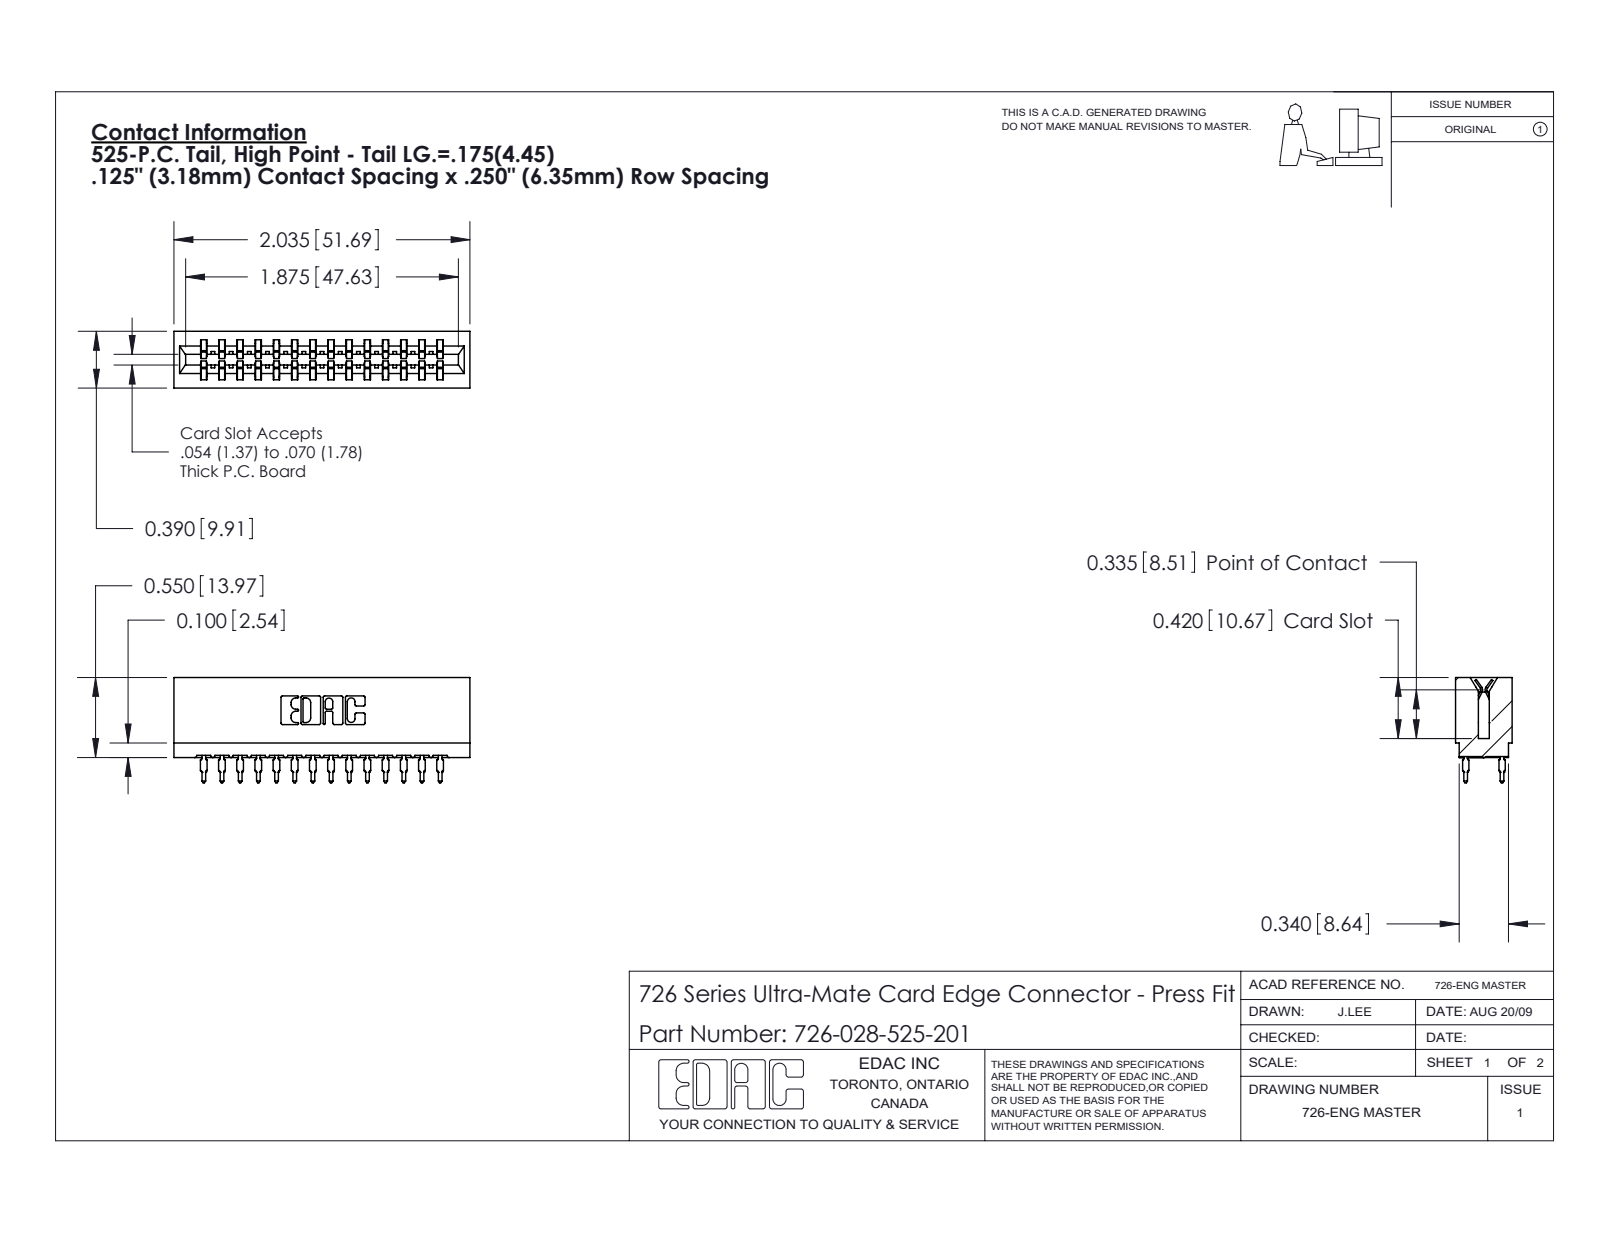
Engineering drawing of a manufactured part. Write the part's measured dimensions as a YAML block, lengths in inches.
part_name: "726-028-525-201; 746-292-001_525; 726 Part_.515 Slot Depth - 01"
step_written_by: "SolidWorks 2020 (CONFIG_CONTROL_DESIGN)"
units: inches
bodies: {solids: 29, faces: 2603, planar: 1343, cylindrical: 532, other: 728}
overall_size: [2.035, 0.724, 0.39]
volume: 0.298
surface_area: 11.76
partial_cylinders:
  - {radius: 0.021, count: 56}
  - {radius: 0.01, count: 22}
  - {radius: 0.015, count: 15}
  - {radius: 0.005, count: 8}
  - {radius: 0.011, count: 8}
  - {radius: 0.007, count: 6}
  - {radius: 0.031, count: 6}
  - {radius: 0.026, count: 3}
face_to_face_distances: [0.057, 0.25, 0.333, 0.39, 0.025, 0.307, 0.125, 0.75, 1.25, 0.5]
